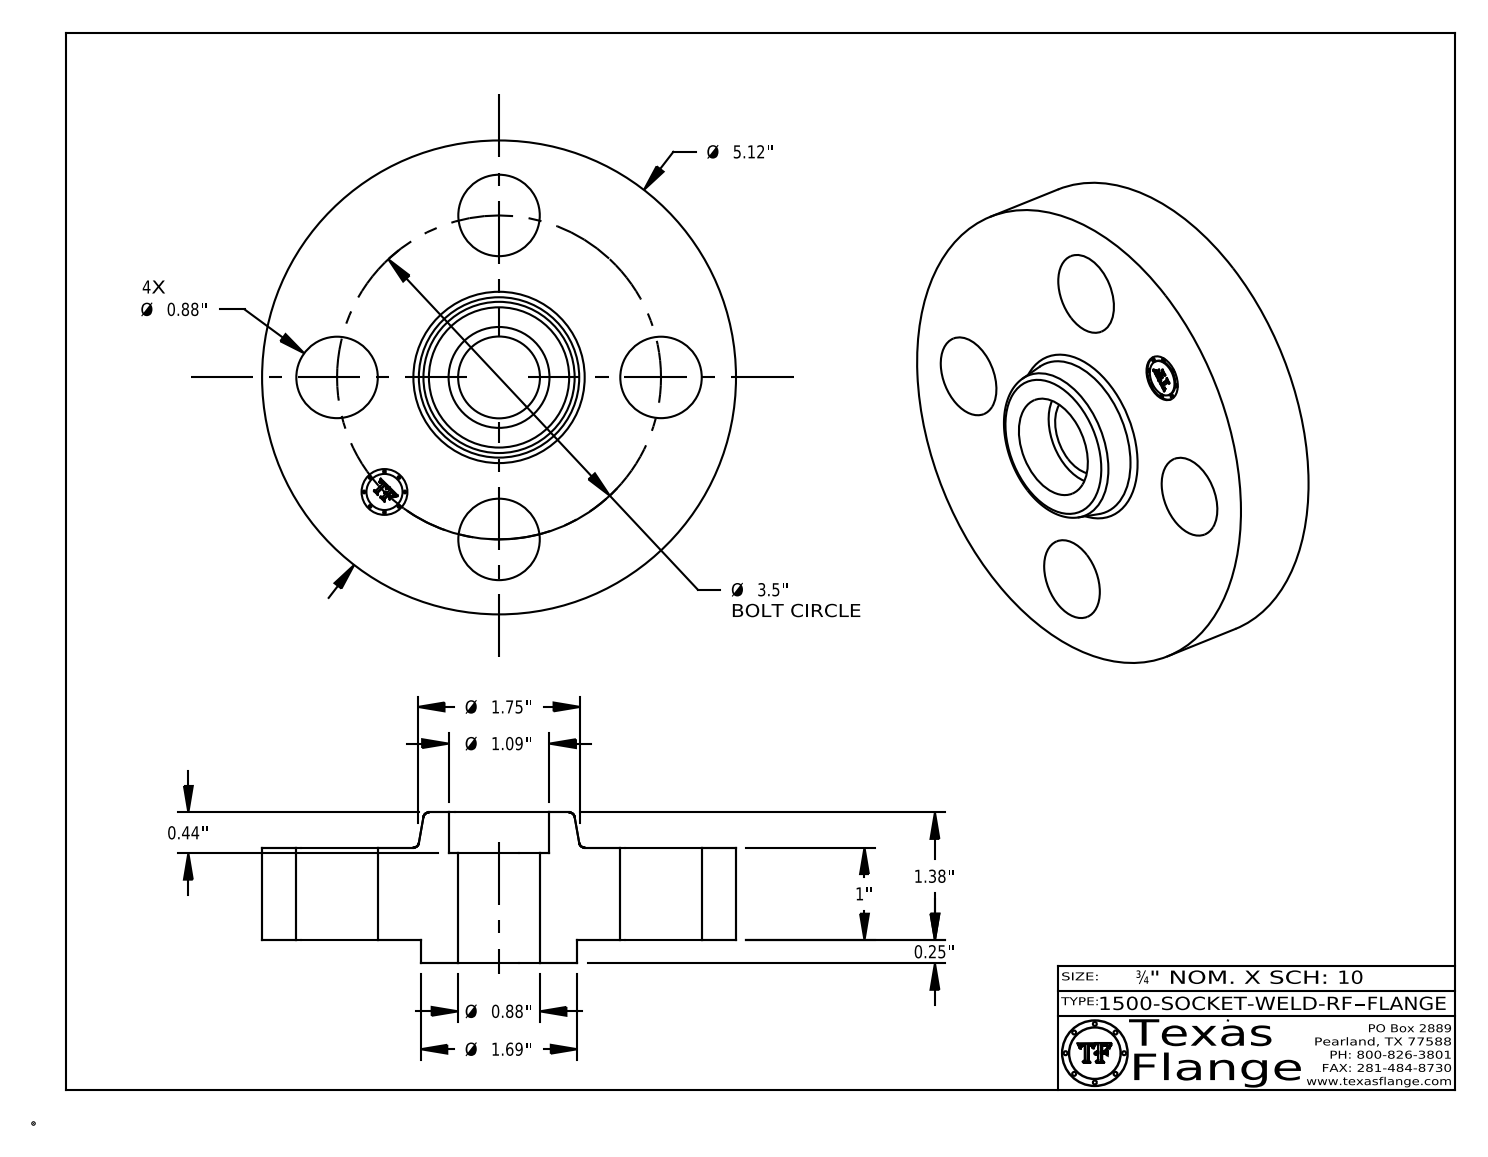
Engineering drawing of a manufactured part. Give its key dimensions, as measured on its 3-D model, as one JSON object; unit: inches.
{"part_name": "1500-SOCKET-WELD-RF", "step_written_by": "CATIA V5 STEP AP214 (AUTOMOTIVE_DESIGN)", "units": "inches", "bodies": {"solids": 1, "faces": 412, "planar": 370, "cylindrical": 36, "other": 6}, "overall_size": [5.12, 5.12, 1.63], "volume_in3": 18.42, "surface_area_in2": 69.97, "round_holes": [[0.88, 4], [0.495, 1], [0.884, 1], [1.09, 1]], "round_bosses_or_shafts": [[0.03, 8], [5.12, 1], [1.69, 1], [0.39, 1]], "face_to_face_distances": [1, 0.25, 1.25, 1.63, 1.38, 0.38, 0.06, 1.19, 0.94, 0.44], "hole_center_spacings": [1.75, 2.475, 1.339, 3.233, 3.5]}
